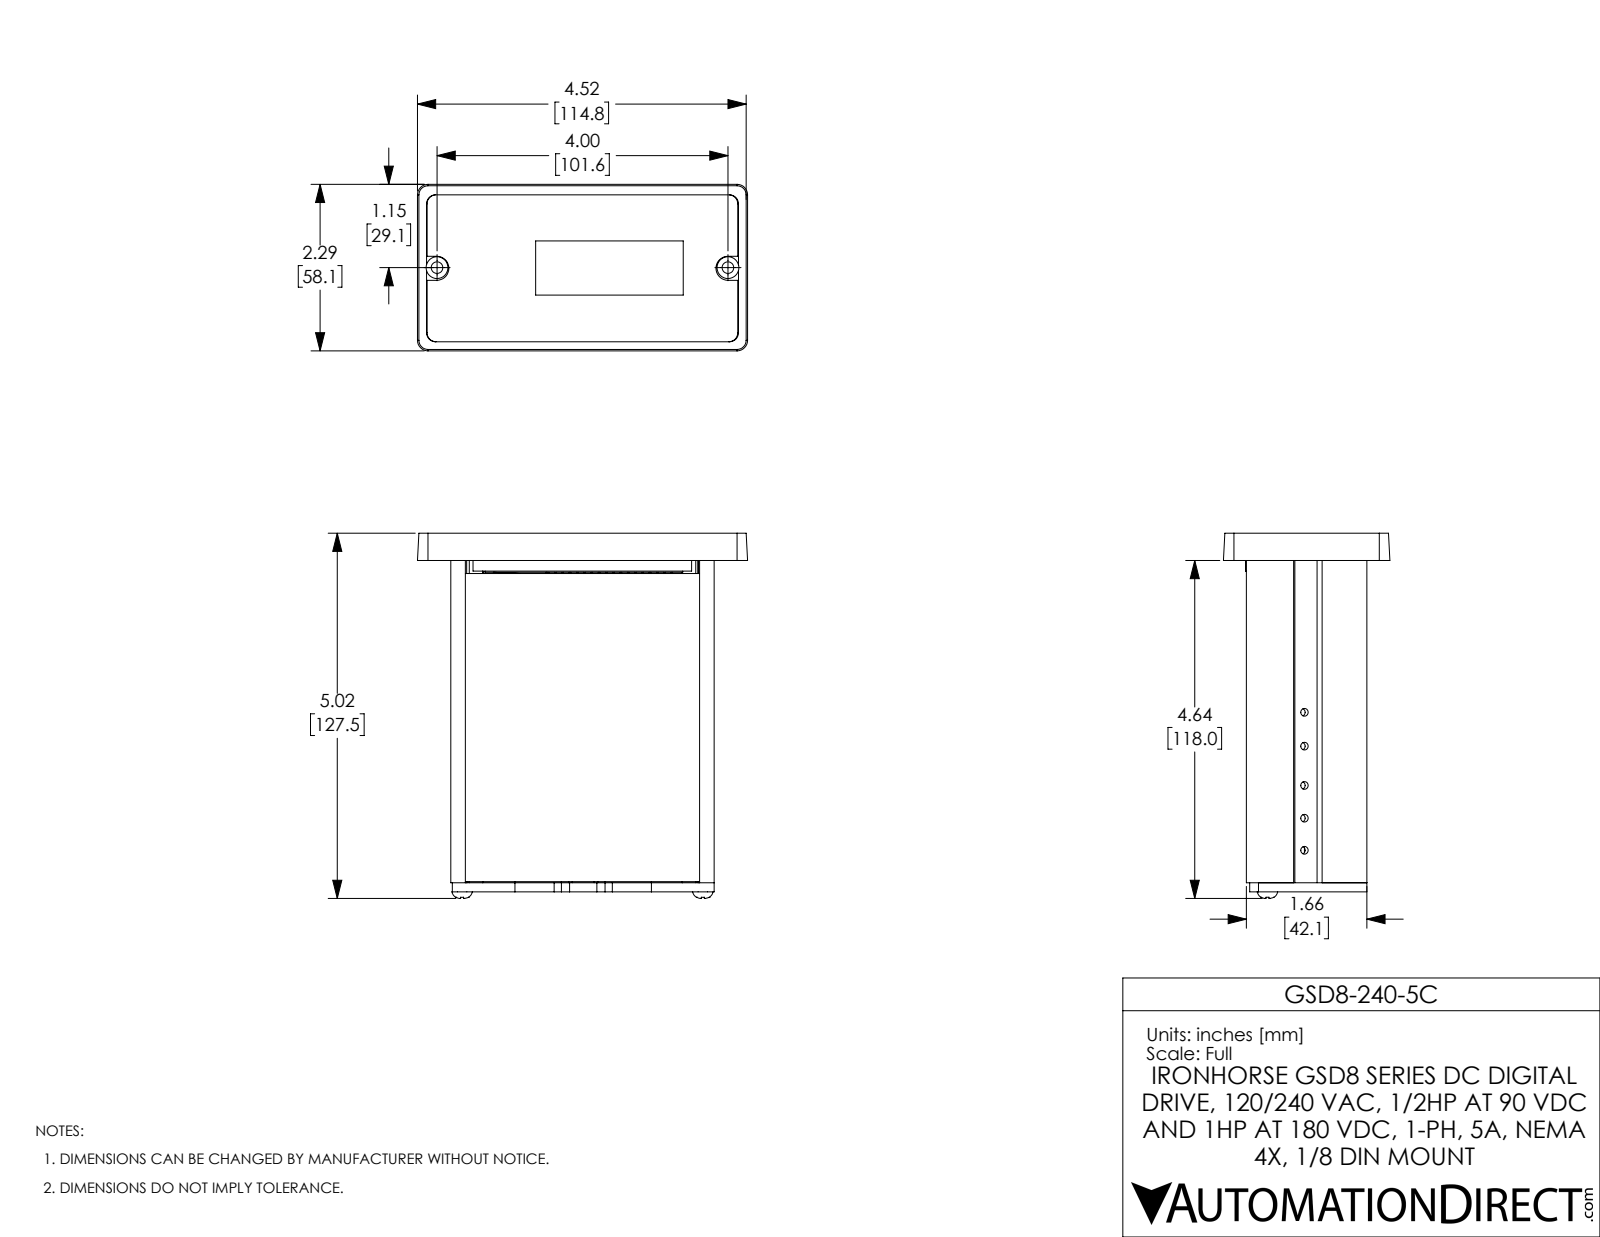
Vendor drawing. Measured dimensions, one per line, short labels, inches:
name: GSD8-240-5C
written by: SolidWorks 2017 (AUTOMOTIVE_DESIGN)
unit: in
bodies: 15 solids, 1227 faces (759 planar, 447 cylindrical, 21 other)
size: 5.019 × 4.539 × 2.289
volume: 9.053 in³; area: 219 in²
holes: 36× ⌀0.033, 13× ⌀0.035, 12× ⌀0.157, 6× ⌀0.02, 6× ⌀0.059, 6× ⌀0.147, 6× ⌀0.16, 5× ⌀0.106, 4× ⌀0.12, 4× ⌀0.285, 3× ⌀0.016, 3× ⌀0.112
bosses: 36× ⌀0.02, 3× ⌀0.247, 2× ⌀0.134
rounds: 18× R0.05, 16× R0.039, 12× R0.125, 10× R0.126, 7× R0.025, 4× R0.016, 4× R0.035, 4× R0.045
face distances: 0.1, 1.521, 0.045, 1.566, 1.421, 1.466, 0.031, 1.313, 0.209, 0.178
hole spacings: 0.197, 0.394, 0.591, 0.787, 0.984, 1.181, 0.1, 0.2
